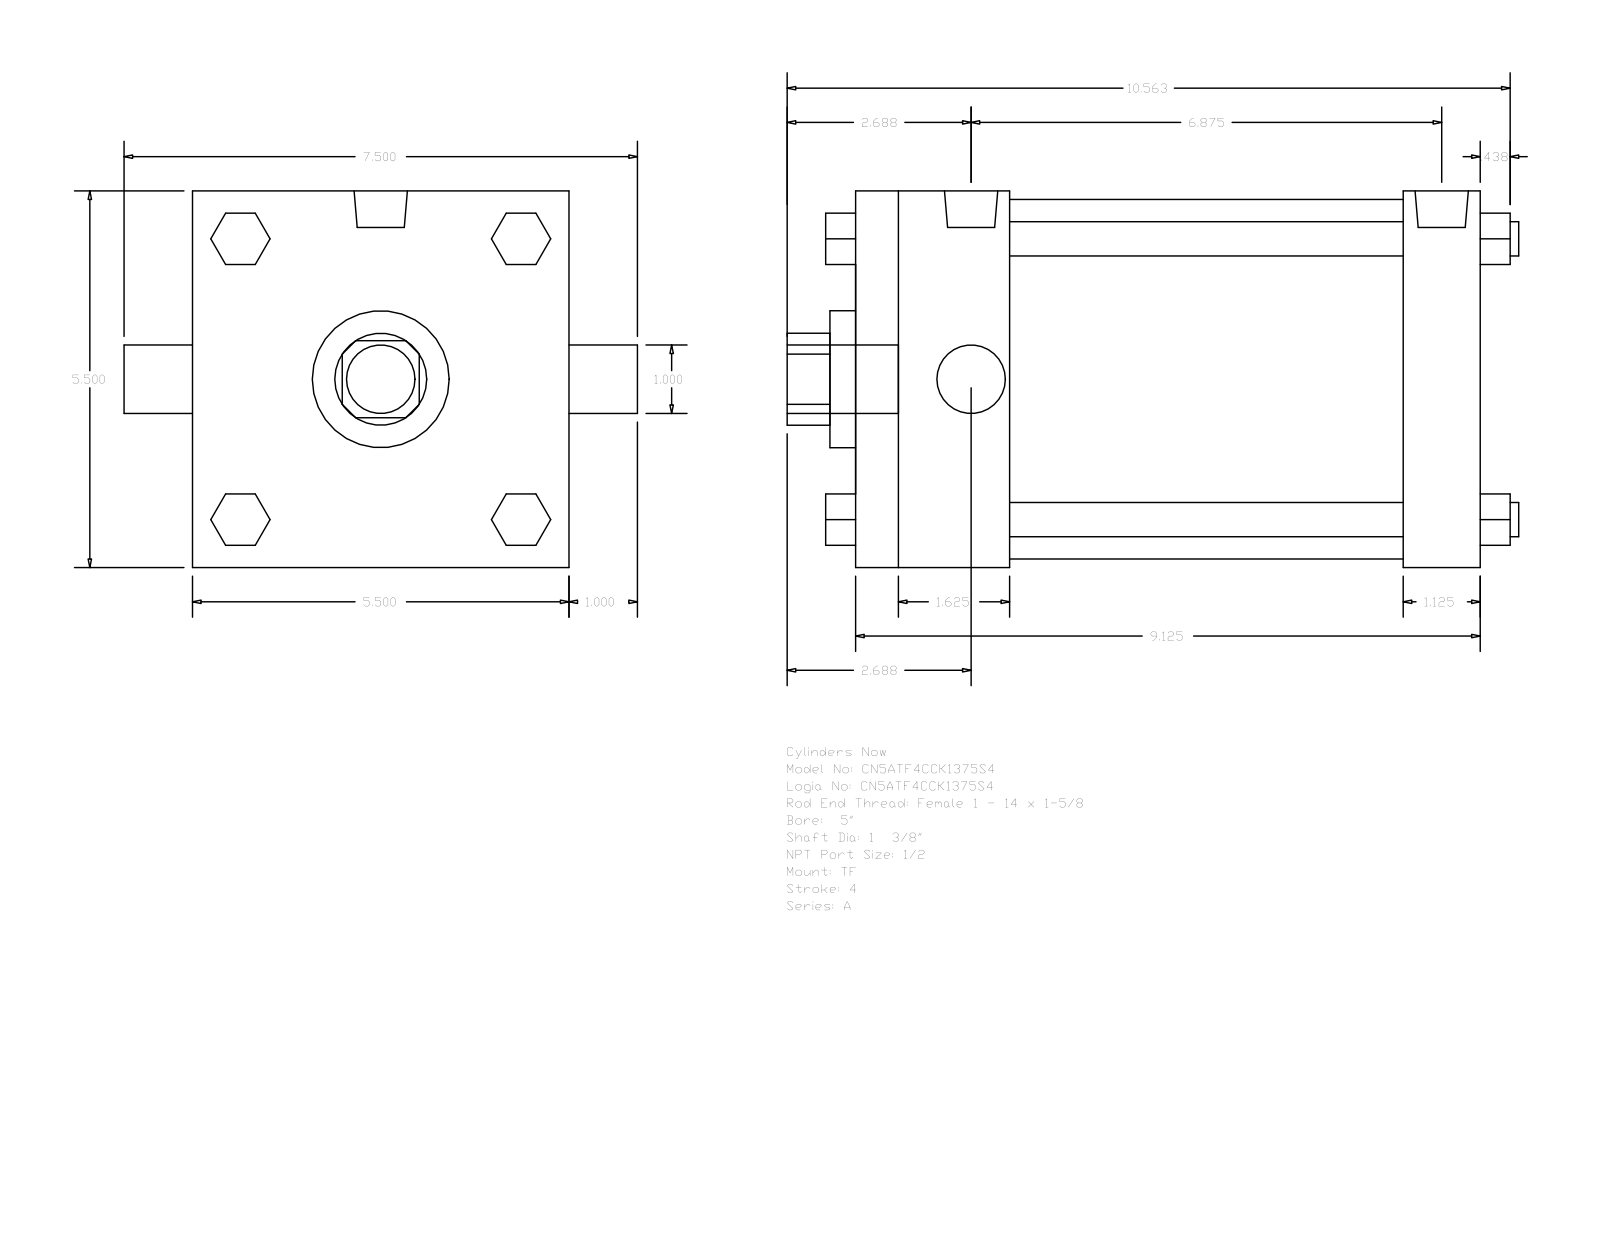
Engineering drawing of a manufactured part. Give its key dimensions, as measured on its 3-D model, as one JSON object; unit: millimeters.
{"part_name": "A_TF__0500_1.375", "step_written_by": "GSSL Pune (CONFIG_CONTROL_DESIGN)", "units": "millimeters", "bodies": {"solids": 0, "faces": 120, "planar": 92, "cylindrical": 28, "other": 0}, "overall_size": [271.46, 190.5, 139.7], "round_holes": [[25.4, 1], [34.92, 1], [50.8, 1], [133.35, 1]], "round_bosses_or_shafts": [[12.7, 4], [8.73, 3], [19.77, 2], [25.4, 1]], "partial_cylinders_radius": [[17.06, 1]], "face_to_face_distances": [139.7, 231.78, 28.58, 203.2, 57.15, 146.05, 174.63, 19.05, 52.07, 90.18]}
